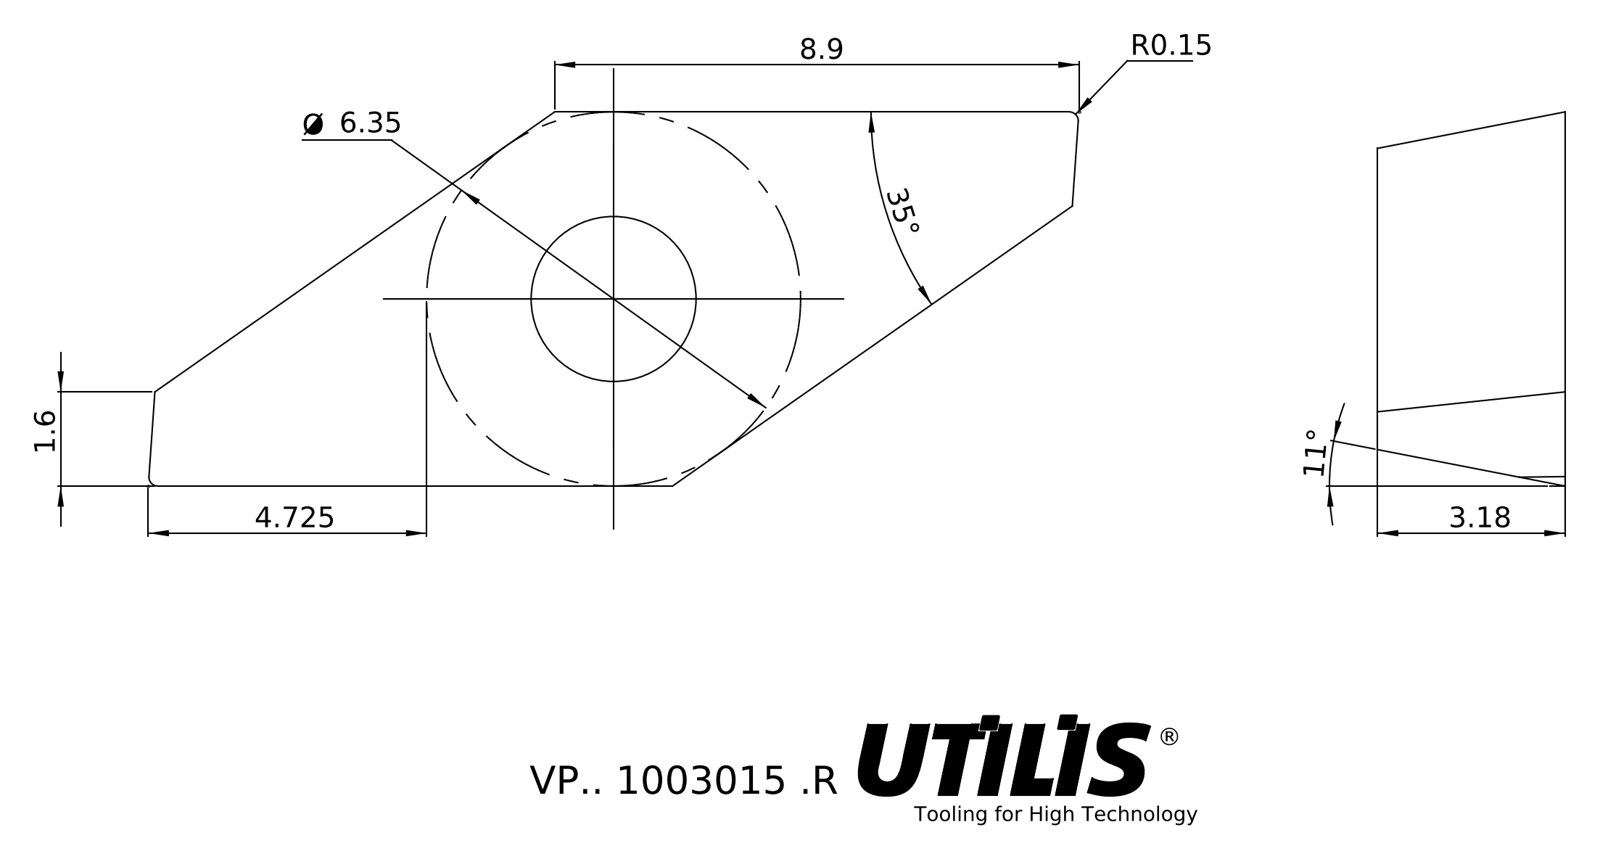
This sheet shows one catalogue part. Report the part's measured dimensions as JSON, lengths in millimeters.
{"part_name": "VP.. 1003015 .R", "step_written_by": "SolidWorks 2016 (AUTOMOTIVE_DESIGN)", "units": "millimeters", "bodies": {"solids": 1, "faces": 13, "planar": 8, "cylindrical": 2, "other": 3}, "overall_size": [15.78, 6.35, 3.18], "volume_mm3": 158, "surface_area_mm2": 242, "round_holes": [[2.8, 1]], "face_to_face_distances": [3.18]}
